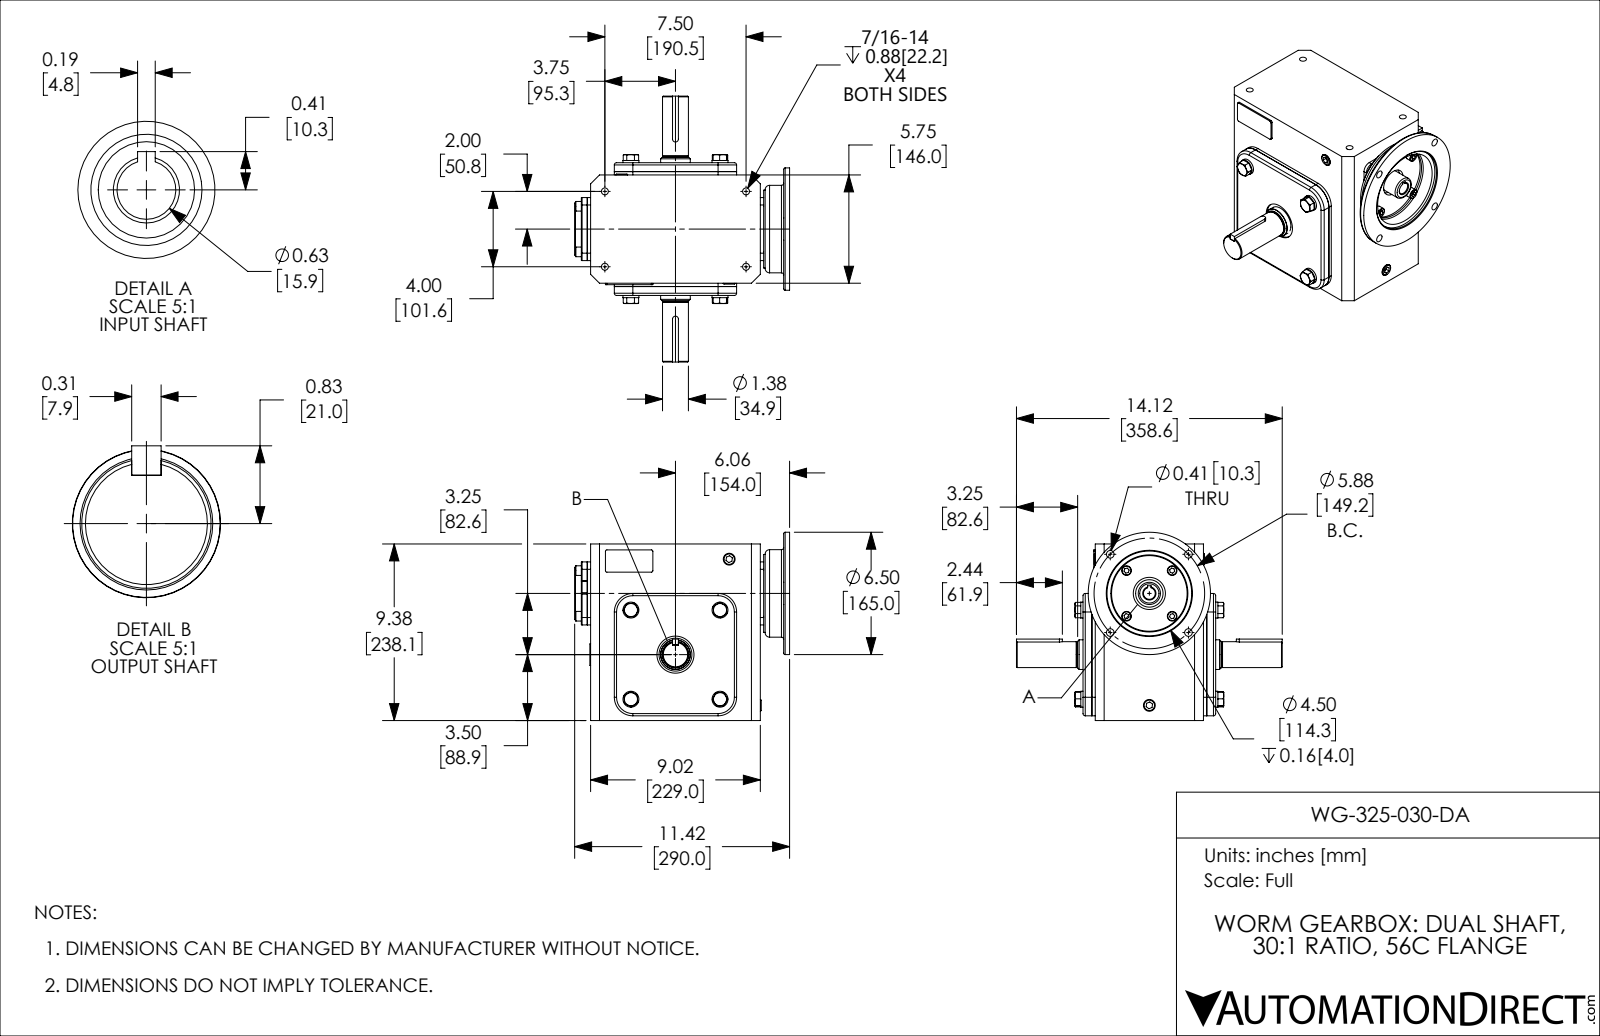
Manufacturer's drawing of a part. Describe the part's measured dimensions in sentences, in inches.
The part is named "WG-325-030-DA". Its 3-D file was written by "SolidWorks 2017 (AUTOMOTIVE_DESIGN)". It is 42 solids with 612 faces: 331 planar, 178 cylindrical and 103 other. Overall it measures 14.118 by 11.417 by 9.998 inches. Its volume is 515.7 cubic inches and its surface area 936.5 square inches. Round holes: 4 of diameter 0.368, 4 of diameter 0.406, 3 of diameter 0.628, 1 of diameter 0.591, 1 of diameter 0.625, 1 of diameter 0.978, 1 of diameter 1.181, 1 of diameter 1.457, 1 of diameter 1.969, 1 of diameter 2.441, 1 of diameter 2.756, 1 of diameter 4.016. Round bosses or shafts: 4 of diameter 0.846, 4 of diameter 0.512, 1 of diameter 6.496, 1 of diameter 4.646, 1 of diameter 4.134, 1 of diameter 2.835, 1 of diameter 1.575, 1 of diameter 1.375. Partial cylindrical surfaces (rounded edges, fillets, slot ends): 8 of radius 0.118, 7 of radius 0.079, 4 of radius 0.394, 4 of radius 0.906, 4 of radius 0.984, 2 of radius 0.02, 2 of radius 0.039, 2 of radius 0.156. The main face-to-face distances are 0.079, 0.177, 6.496, 0.394, 6.969, 0.472, 6.575, 6.398, 0.571, 0.65. The hole center spacings are 2.937, 4.154, 2.385, 4, 4.389, 5.718, 5.817, 5.875.
